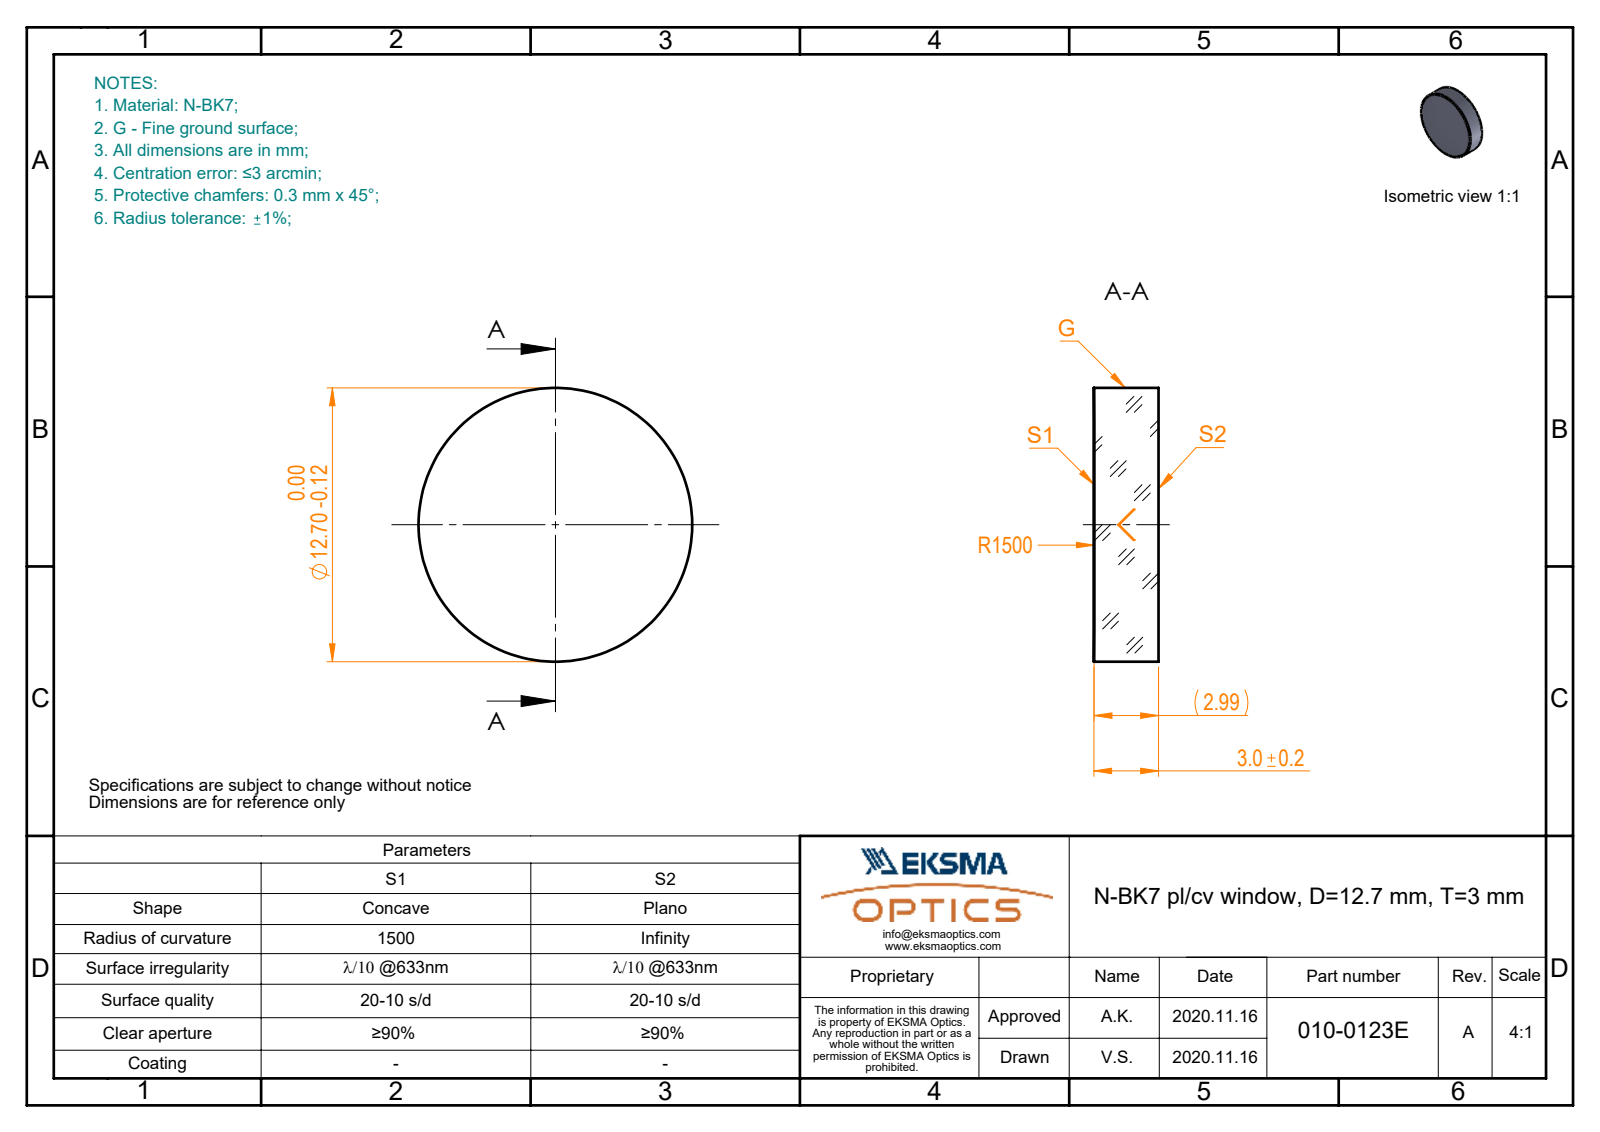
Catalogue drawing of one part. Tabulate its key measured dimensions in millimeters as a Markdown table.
| quantity | value |
| --- | --- |
| part name | 010-0123E_N-BK7_PCV_window |
| STEP written by | SolidWorks 2019 (CONFIG_CONTROL_DESIGN) |
| units | millimeters |
| bodies | 1 solid, 5 faces (1 planar, 2 cylindrical, 2 other) |
| overall size | 12.7 × 12.7 × 3 |
| volume | 379 mm³ |
| surface area | 373 mm² |
| round bosses / shafts (diameter × count) | 12.7 × 1 |
